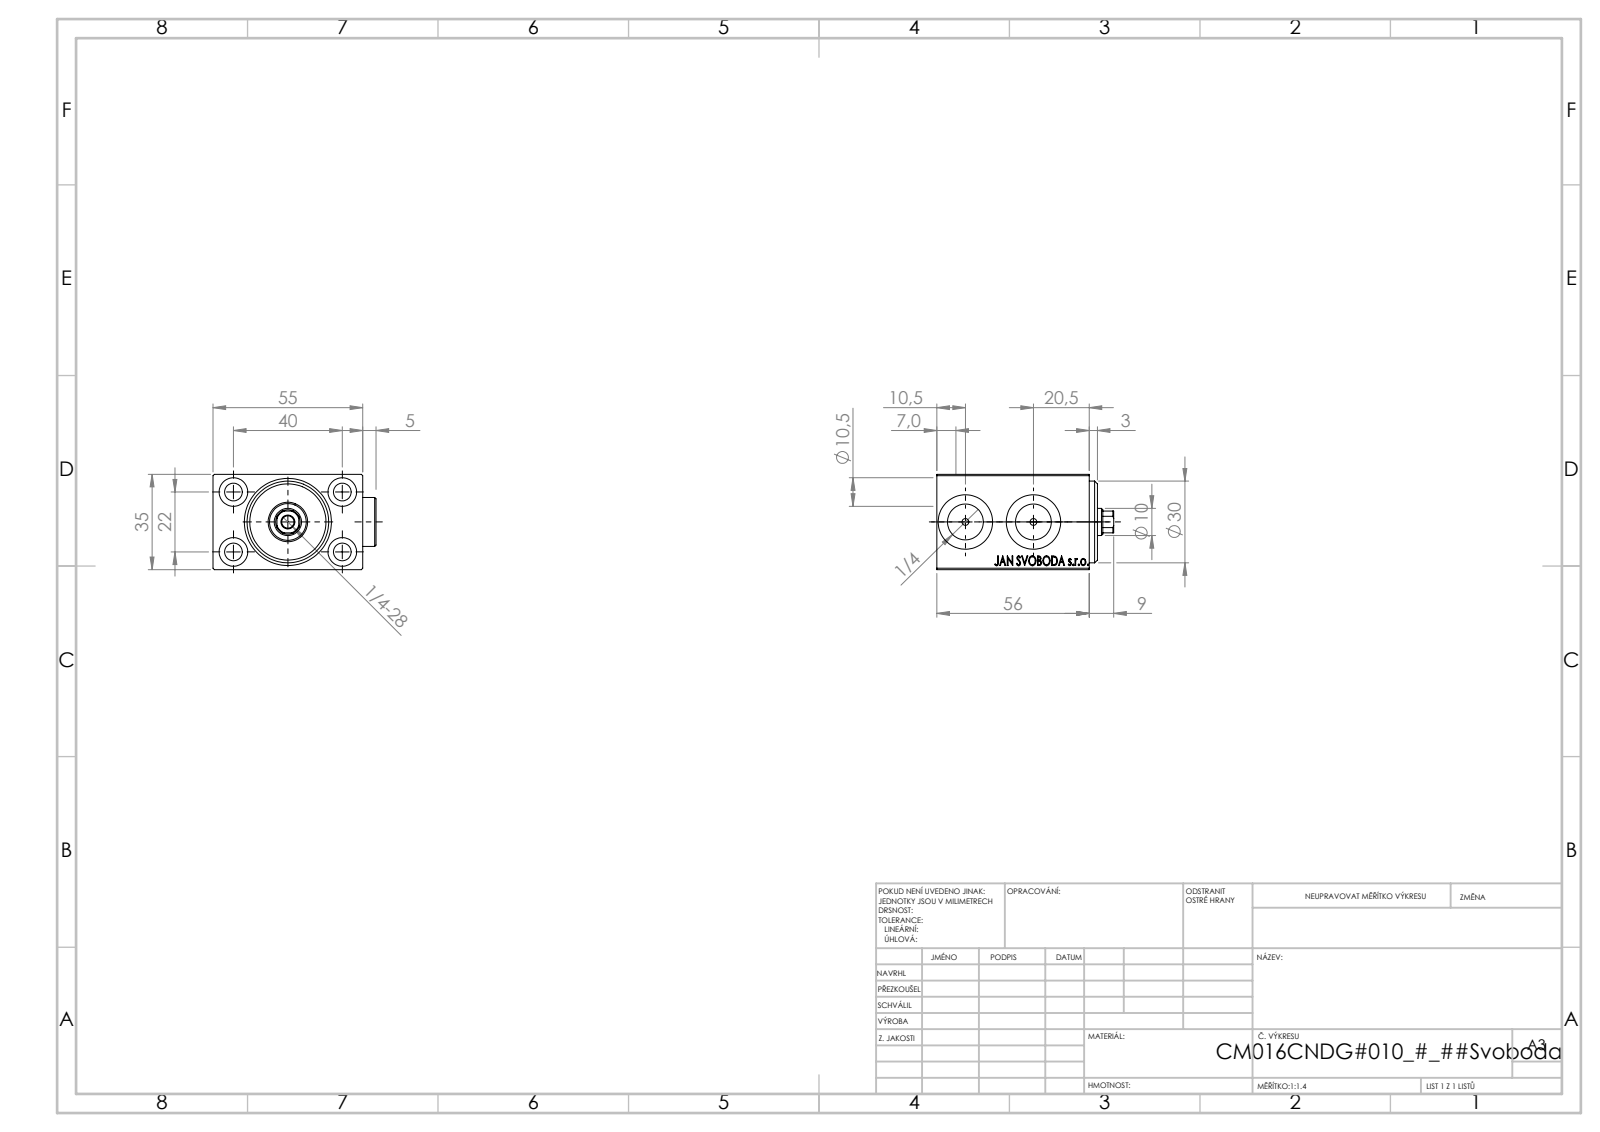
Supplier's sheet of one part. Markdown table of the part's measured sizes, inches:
| quantity | value |
| --- | --- |
| part name | Zatka_OIL_PORT; V450CM_C_Body; V450CM_C_VCP; V450CM_VC_B |
| STEP written by | SolidWorks 2019 (CONFIG_CONTROL_DESIGN) |
| units | inches |
| bodies | 5 solids, 919 faces (443 planar, 78 cylindrical, 398 other) |
| overall size | 2.559 × 2.358 × 1.378 |
| volume | 5.689 in³ |
| surface area | 48.64 in² |
| round holes (diameter × count) | 0.256 × 4, 0.413 × 4, 0.098 × 2, 0.518 × 2, 0.787 × 2, 0.177 × 1, 0.394 × 1, 0.531 × 1, 0.571 × 1, 0.63 × 1, 0.709 × 1, 1.181 × 1 |
| round bosses / shafts (diameter × count) | 0.709 × 2 |
| partial cylindrical surfaces (radius × count) | 0.177 × 1 |
| main face-to-face distances | 1.378, 0.197, 2.008, 2.165, 2.161, 2.205, 0.079, 1.654, 0.118, 0.315 |
| hole center spacings | 0.899, 0.866, 1.575, 1.797, 0.984 |
